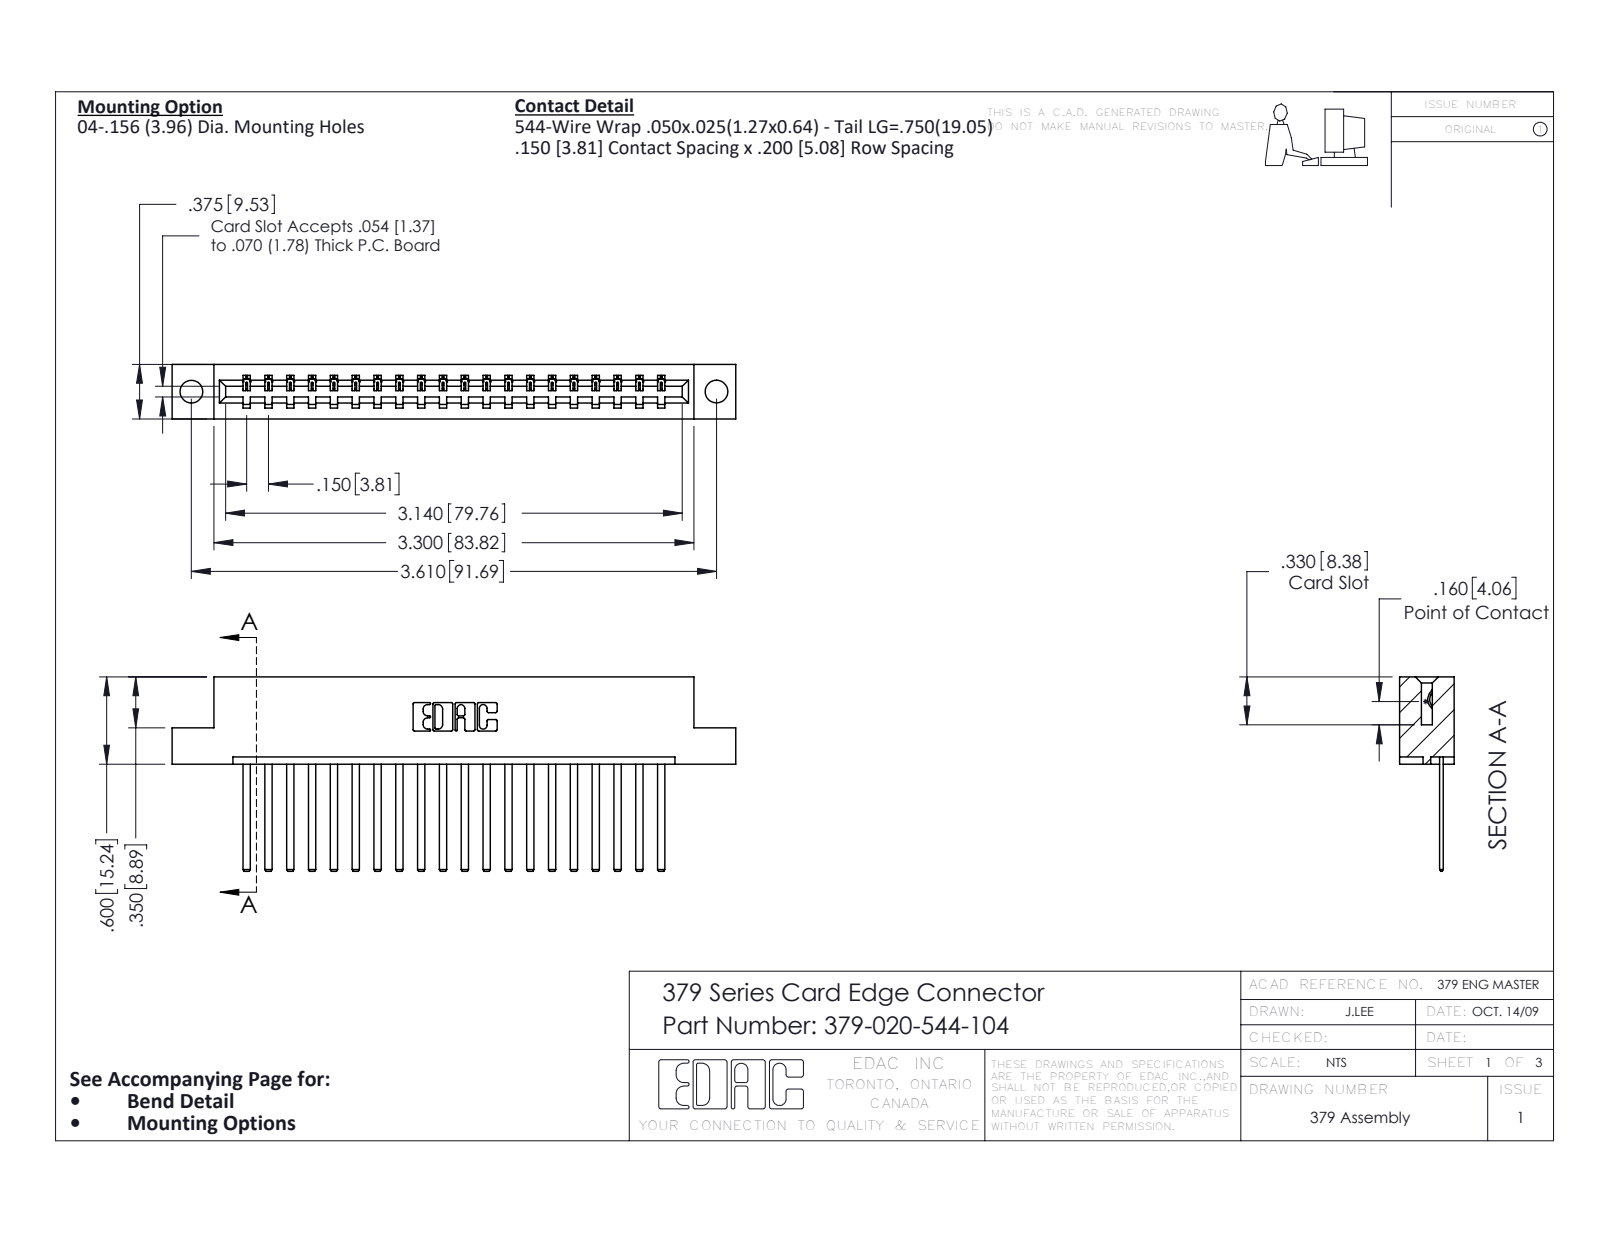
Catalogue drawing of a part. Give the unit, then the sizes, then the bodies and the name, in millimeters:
Units: millimetres
Overall size (bounding box): 98.4 × 34 × 9.5
Round holes (diameter × count): ⌀4 ×2
Partial cylindrical surfaces — rounded edges, fillets, slot ends (radius × count): R0.2 ×40, R0.3 ×22, R0.2 ×6, R0.8 ×6, R0.7 ×3, R0.4 ×1, R0.6 ×1, R0.6 ×1
Main face-to-face distances: 7.6, 1.9, 9.5, 15.2, 7, 2.5, 0.6, 3.8, 5.7, 11.4
Hole centre spacings: 91.7
Volume: 10 200 mm³ · Surface area: 10 910 mm²
Bodies: 21 solids, 1154 faces (830 planar, 324 cylindrical, 0 other)
Part name (STEP PRODUCT): 379-020-544-104; 345-292-001_345-293-144; 379 Part_Flush - .156 Dia - TH
STEP written by: SolidWorks 2016 (CONFIG_CONTROL_DESIGN)
